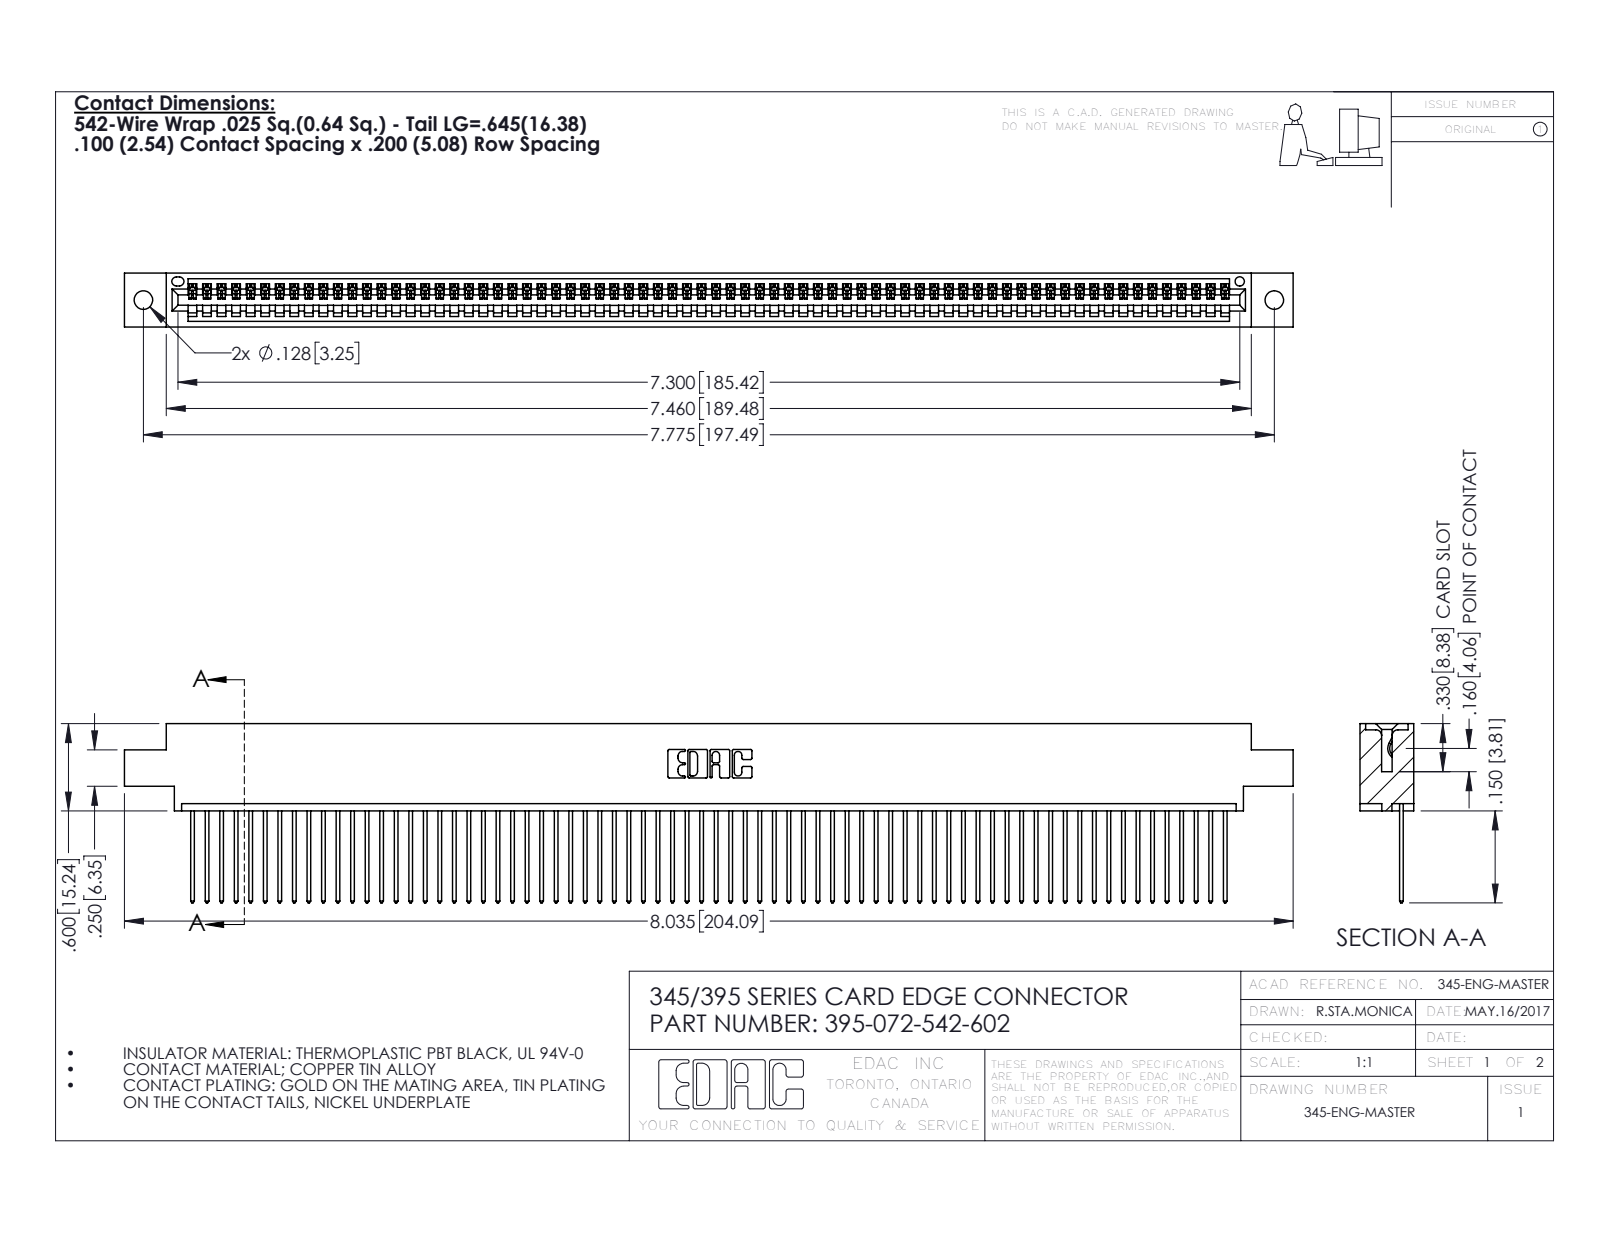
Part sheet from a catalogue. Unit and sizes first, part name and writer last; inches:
Units: inches
Overall size (bounding box): 8.035 × 1.232 × 0.37
Round holes (diameter × count): ⌀0.128 ×2, ⌀0.064 ×1
Partial cylindrical surfaces — rounded edges, fillets, slot ends (radius × count): R0.006 ×144, R0.01 ×144, R0.01 ×22, R0.007 ×6, R0.031 ×6, R0.026 ×3, R0.031 ×2, R0.04 ×2
Main face-to-face distances: 0.072, 0.298, 0.37, 0.098, 0.272, 0.025, 0.2, 0.225, 0.175, 0.149
Hole centre spacings: 0.27, 7.539, 7.775
Volume: 1.199 in³ · Surface area: 42.43 in²
Bodies: 73 solids, 4306 faces (2964 planar, 1342 cylindrical, 0 other)
Part name (STEP PRODUCT): 345-292-001_345-293-142; 395-072-542-602; 345 Part_0.170 Offset - 0.128 Dia
STEP written by: SolidWorks 2016 (CONFIG_CONTROL_DESIGN)
